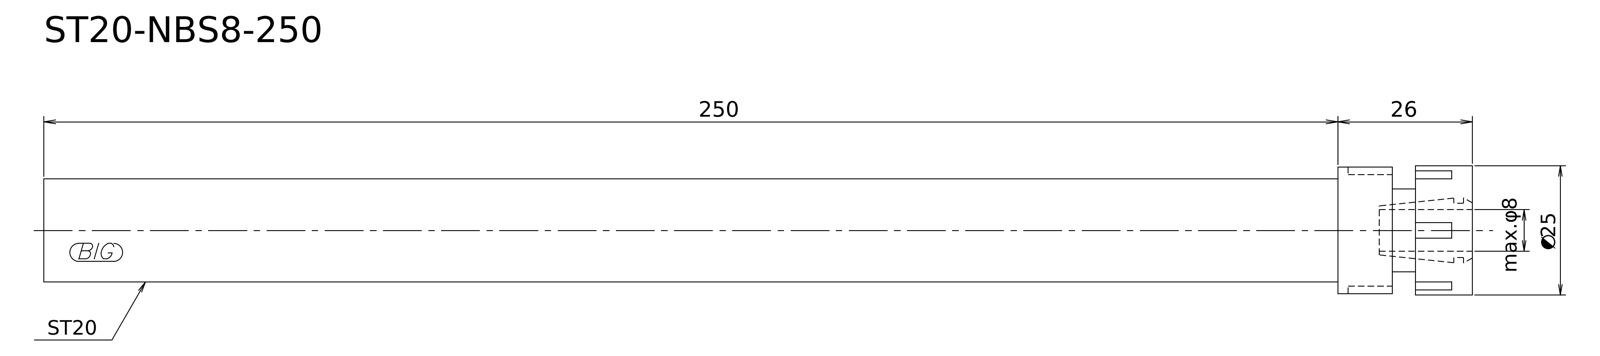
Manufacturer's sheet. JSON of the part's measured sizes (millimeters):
{"step_written_by": "Kubotek KeyCreator V8.5.1 (14335) (CONFIG_CONTROL_DESIGN)", "units": "millimeters", "bodies": {"solids": 1, "faces": 9, "planar": 5, "cylindrical": 4, "other": 0}, "overall_size": [276, 25, 25], "volume_mm3": 89794, "surface_area_mm2": 19129, "round_bosses_or_shafts": [[25, 1], [24.5, 1], [20, 1], [16, 1]], "face_to_face_distances": [276, 11, 265, 15.5, 4.5, 260.5, 26, 15, 10.5, 250]}
